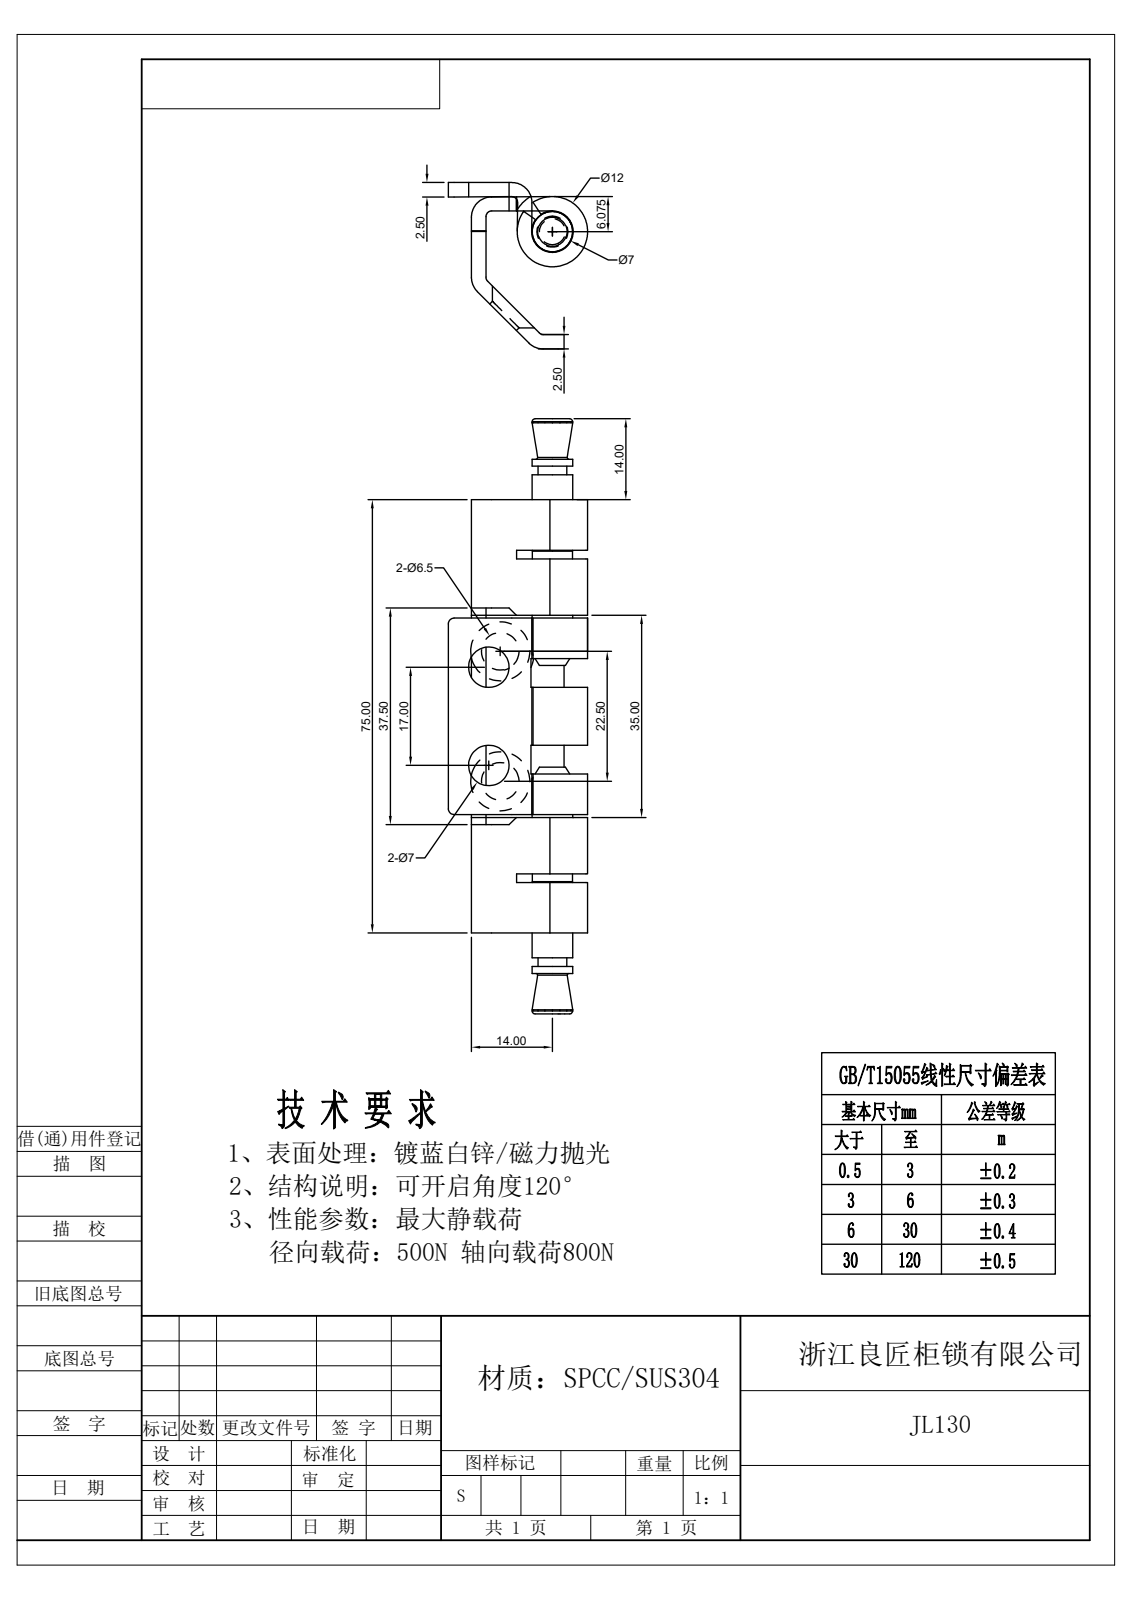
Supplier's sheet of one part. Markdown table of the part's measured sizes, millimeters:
| quantity | value |
| --- | --- |
| STEP written by | Rhino 8.5 (CONFIG_CONTROL_DESIGN) |
| units | millimeters |
| bodies | 4 solids, 160 faces (77 planar, 59 cylindrical, 24 other) |
| overall size | 233.65 × 82.43 × 28.8 |
| volume | 14 642 mm³ |
| surface area | 13 660 mm² |
| round holes (diameter × count) | 6.5 × 2, 7 × 2, 7.17 × 1 |
| round bosses / shafts (diameter × count) | 12.17 × 1, 7 × 1, 6.98 × 1, 5 × 1 |
| partial cylindrical surfaces (radius × count) | 1 × 8, 3.5 × 4, 7.17 × 1 |
| main face-to-face distances | 2.5, 2.52, 10.25, 20, 27.5, 26.3, 54.5, 4.92, 23.88, 28.8 |
| hole center spacings | 17, 22.5 |
